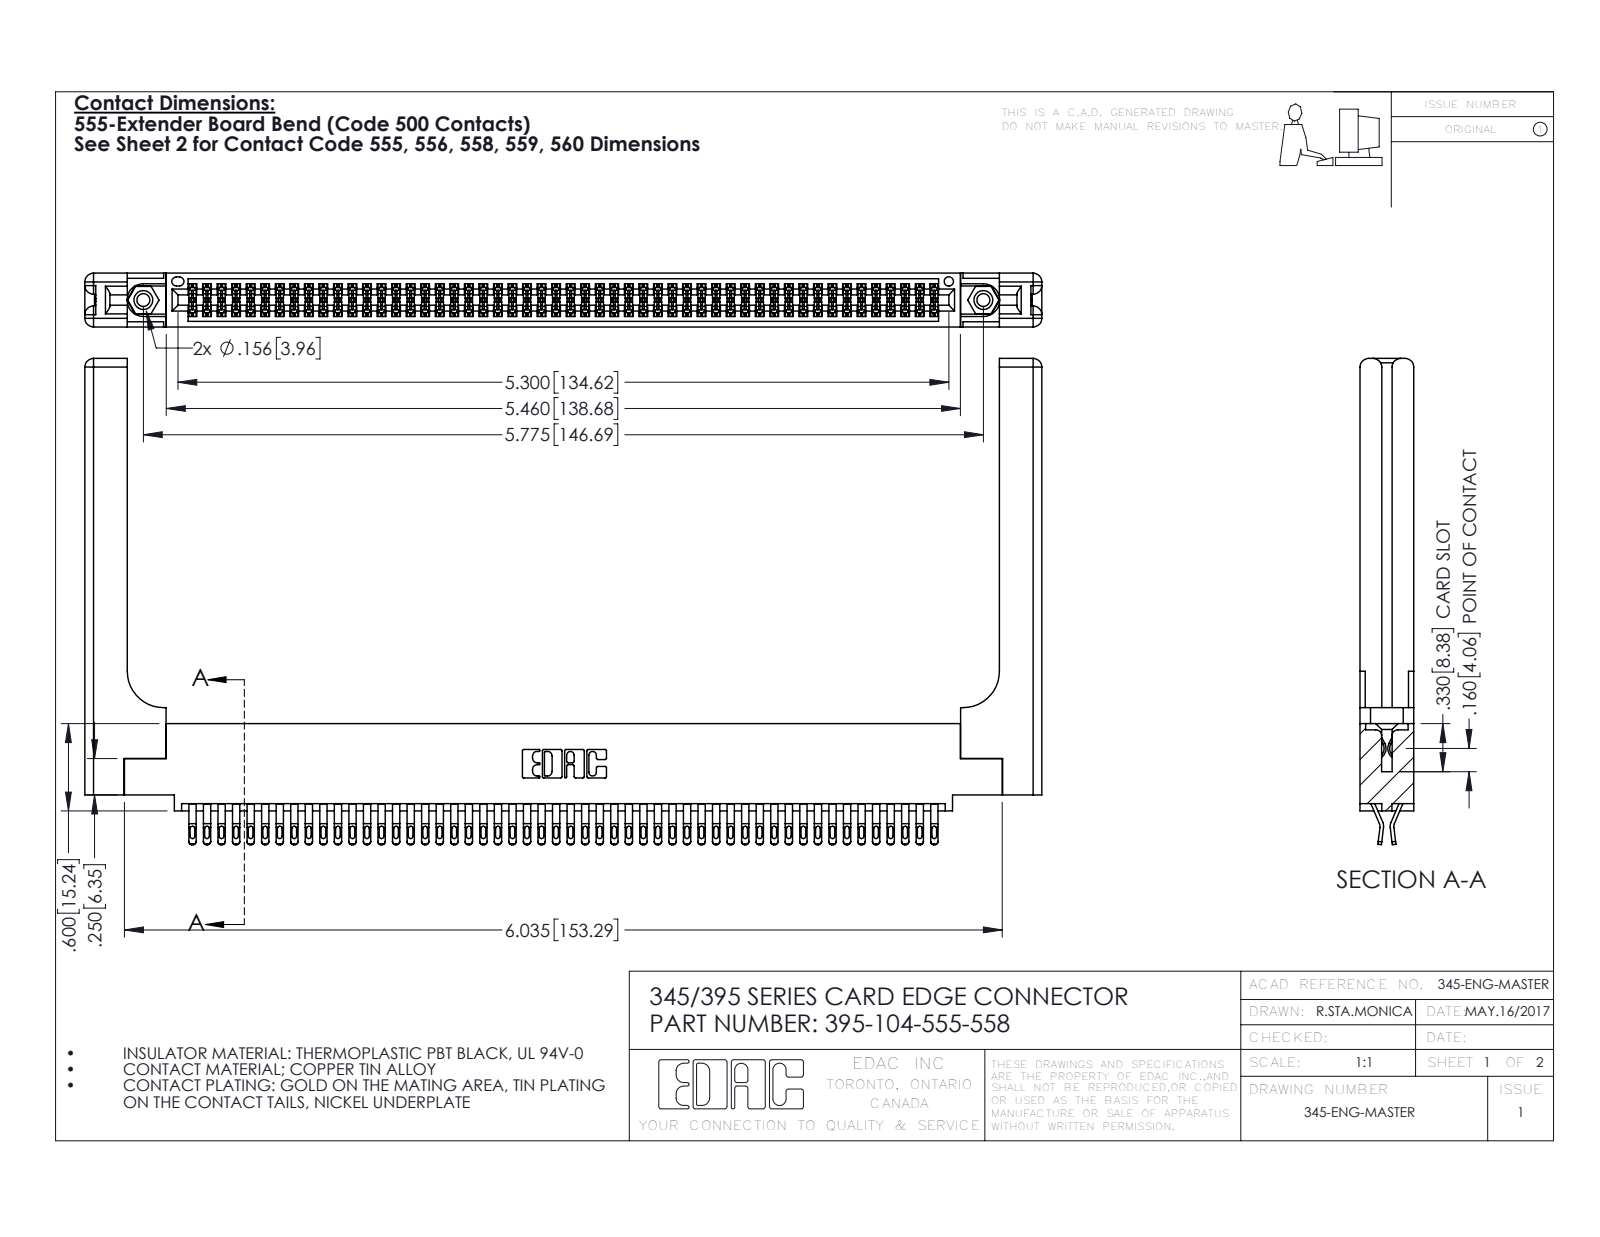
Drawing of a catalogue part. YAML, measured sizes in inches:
part_name: "345-220-058_345-220-058; 345-292-001_555 Tail; 345-250-001_345-250-001-102; 395-104-555-558 (+1 more)"
step_written_by: "SolidWorks 2016 (CONFIG_CONTROL_DESIGN)"
units: inches
bodies: {solids: 109, faces: 6210, planar: 3456, cylindrical: 2694, other: 60}
overall_size: [6.579, 3.342, 0.37]
volume: 1.527
surface_area: 47.84
round_holes:
  - {diameter: 0.089, count: 2}
  - {diameter: 0.125, count: 2}
  - {diameter: 0.156, count: 2}
  - {diameter: 0.064, count: 1}
round_bosses_or_shafts:
  - {diameter: 0.155, count: 2}
partial_cylinders:
  - {radius: 0.016, count: 260}
  - {radius: 0.02, count: 208}
  - {radius: 0.006, count: 156}
  - {radius: 0.01, count: 22}
  - {radius: 0.06, count: 16}
  - {radius: 0.007, count: 6}
  - {radius: 0.031, count: 6}
  - {radius: 0.026, count: 3}
face_to_face_distances: [0.072, 0.298, 0.37, 0.025, 0.098, 0.272, 0.2, 0.225, 0.148, 0.15]
hole_center_spacings: [0.27, 5.539, 5.775]
